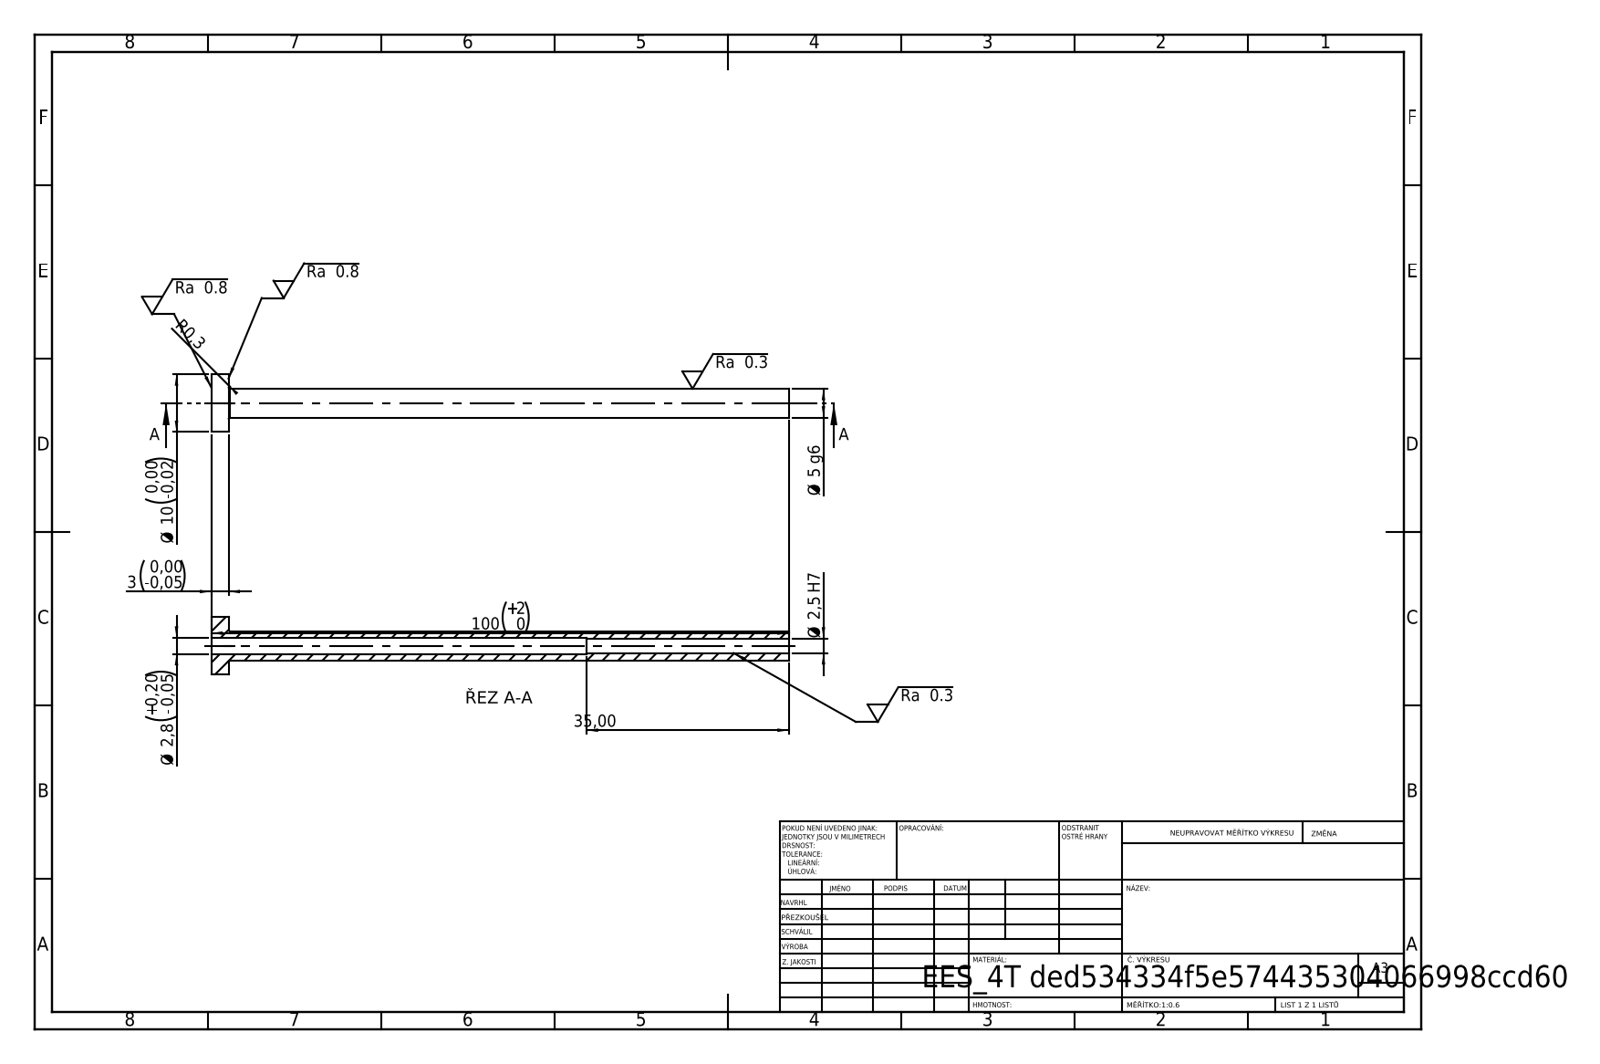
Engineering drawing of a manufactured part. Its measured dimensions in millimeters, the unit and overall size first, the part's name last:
Units: millimetres
Overall size (bounding box): 100 × 10 × 10
Round holes (diameter × count): ⌀2.5 ×1, ⌀2.8 ×1
Round bosses / shafts (diameter × count): ⌀10 ×1, ⌀5 ×1
Main face-to-face distances: 3, 100, 97, 65, 62, 35
Volume: 1 568 mm³ · Surface area: 2 610 mm²
Bodies: 1 solid, 14 faces (4 planar, 8 cylindrical, 2 other)
STEP written by: SolidWorks 2019 (CONFIG_CONTROL_DESIGN)
